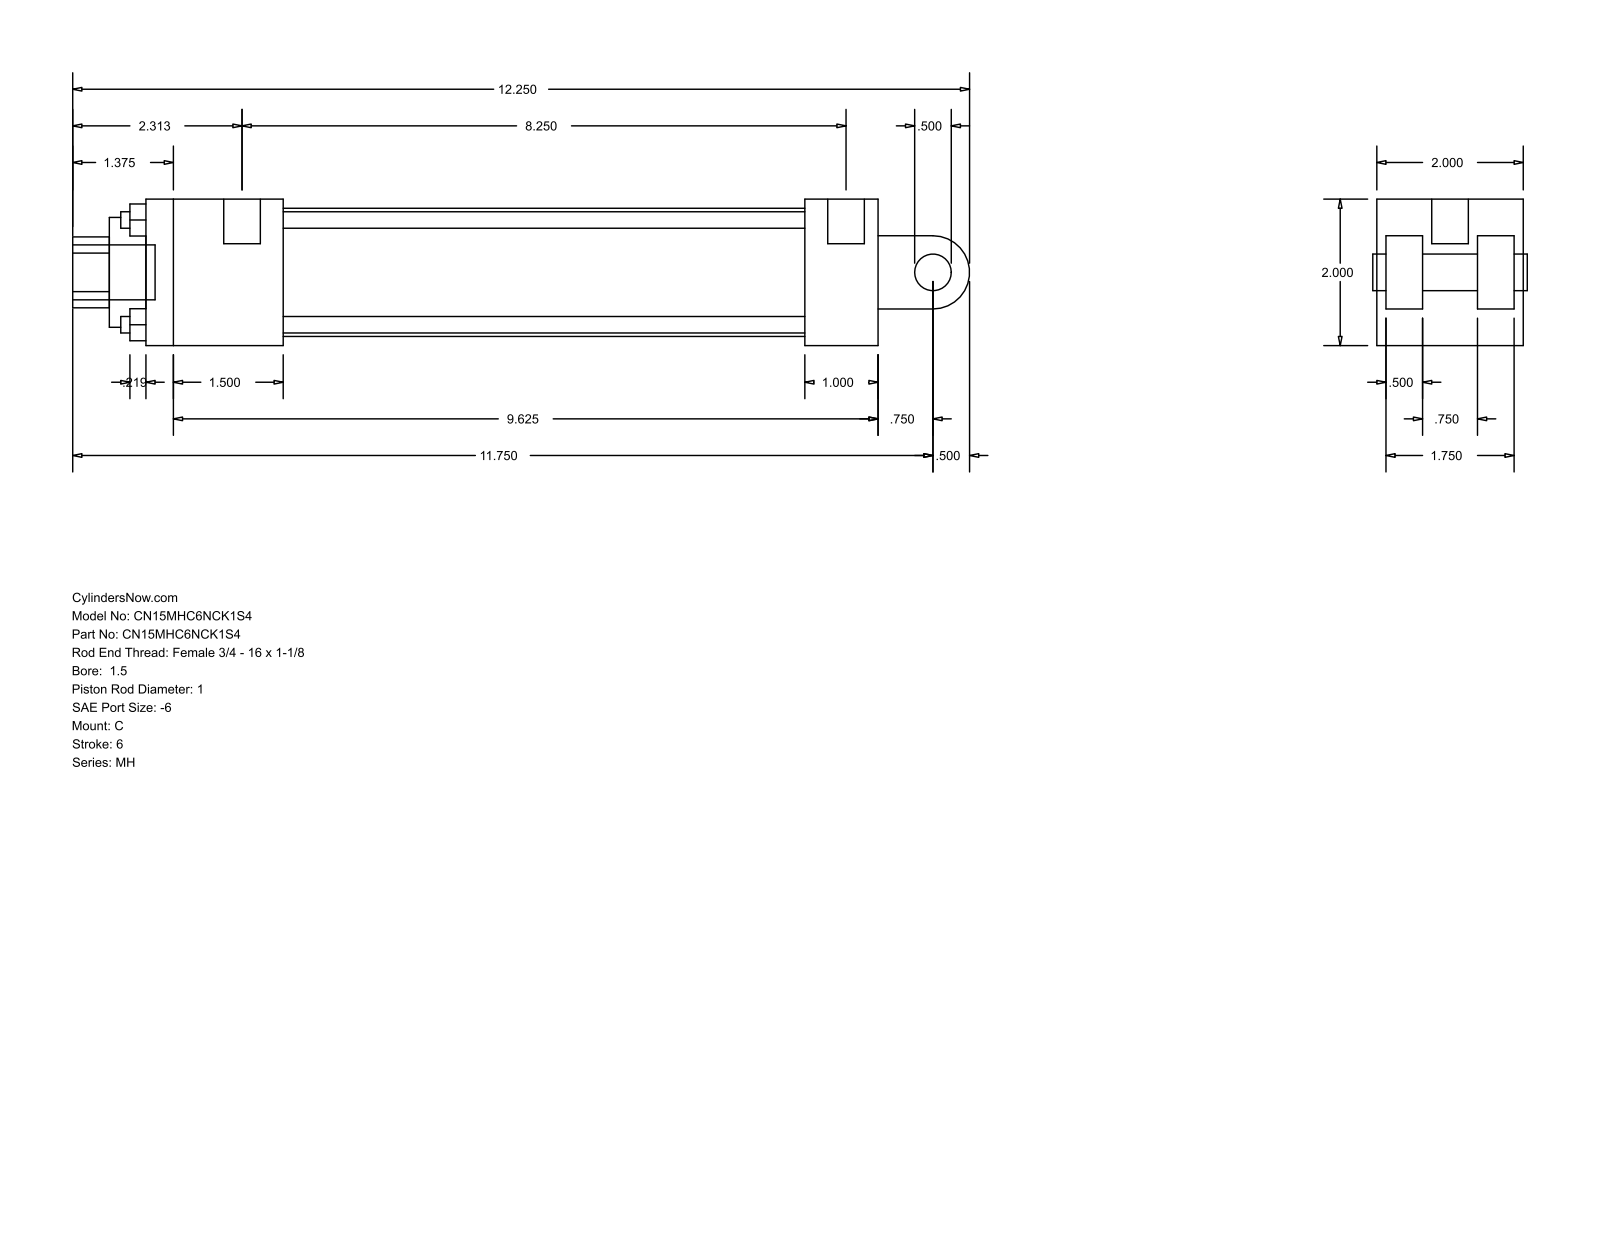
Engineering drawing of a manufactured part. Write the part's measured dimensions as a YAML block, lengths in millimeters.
part_name: "MH_C__0150_1"
step_written_by: "GSSL Pune (CONFIG_CONTROL_DESIGN)"
units: millimeters
bodies: {solids: 0, faces: 99, planar: 70, cylindrical: 29, other: 0}
overall_size: [311.15, 50.8, 50.8]
round_holes:
  - {diameter: 5.71, count: 4}
  - {diameter: 5.56, count: 2}
  - {diameter: 12.7, count: 1}
  - {diameter: 25.4, count: 1}
  - {diameter: 38.1, count: 1}
  - {diameter: 44.45, count: 1}
round_bosses_or_shafts:
  - {diameter: 12.7, count: 2}
  - {diameter: 5.56, count: 2}
  - {diameter: 19.05, count: 1}
partial_cylinders:
  - {radius: 12.29, count: 1}
  - {radius: 12.7, count: 1}
face_to_face_distances: [50.8, 12.7, 47.63, 3.17, 15.87, 25.4, 34.93, 31.76, 254, 38.1]
hole_center_spacings: [25.68, 36.32, 51.36]
